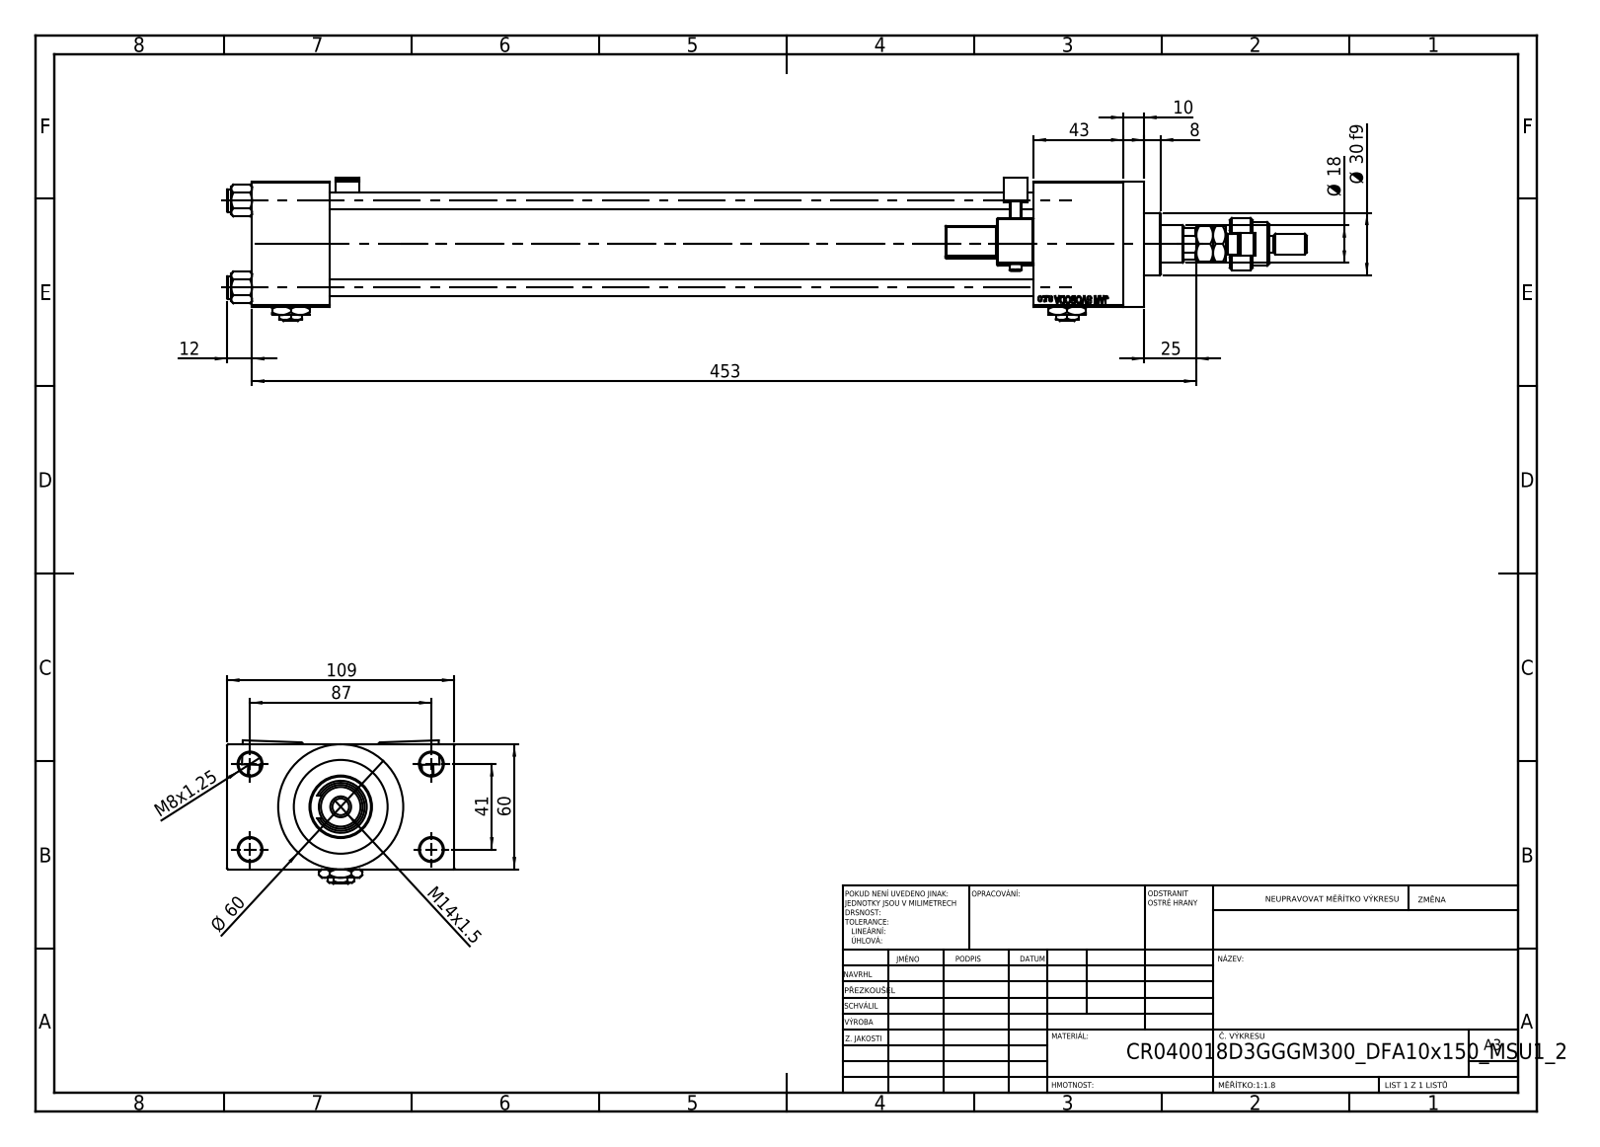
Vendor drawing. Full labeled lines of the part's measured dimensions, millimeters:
Part name (STEP PRODUCT): V215CR_D_Body; V215CR_MSU; V215_VC_A; V215CR_D_TYCINKA (+5 more)
STEP written by: SolidWorks 2019 (CONFIG_CONTROL_DESIGN)
Units: millimetres
Bodies: 17 solids, 1445 faces (632 planar, 173 cylindrical, 640 other)
Overall size (bounding box): 518 × 109 × 68.9
Volume: 809 245 mm³ · Surface area: 261 079 mm²
Round holes (diameter × count): ⌀8 ×4, ⌀11 ×4, ⌀7 ×2, ⌀16.66 ×2, ⌀24 ×2, ⌀8.5 ×1, ⌀18 ×1, ⌀21 ×1, ⌀31 ×1, ⌀40 ×1, ⌀45 ×1
Round bosses / shafts (diameter × count): ⌀11 ×4, ⌀6 ×2, ⌀60 ×1, ⌀46 ×1, ⌀30 ×1, ⌀25 ×1, ⌀16 ×1, ⌀10 ×1
Partial cylindrical surfaces — rounded edges, fillets, slot ends (radius × count): R0.5 ×48, R1 ×2, R2.5 ×2, R4 ×2, R5.5 ×1, R8.5 ×1, R8.75 ×1
Main face-to-face distances: 60, 338, 24.5, 84.5, 37, 375, 43, 418, 381, 109
Hole centre spacings: 22.65, 29.49, 41.7, 47.15, 48.09, 64.35, 76.49, 41
